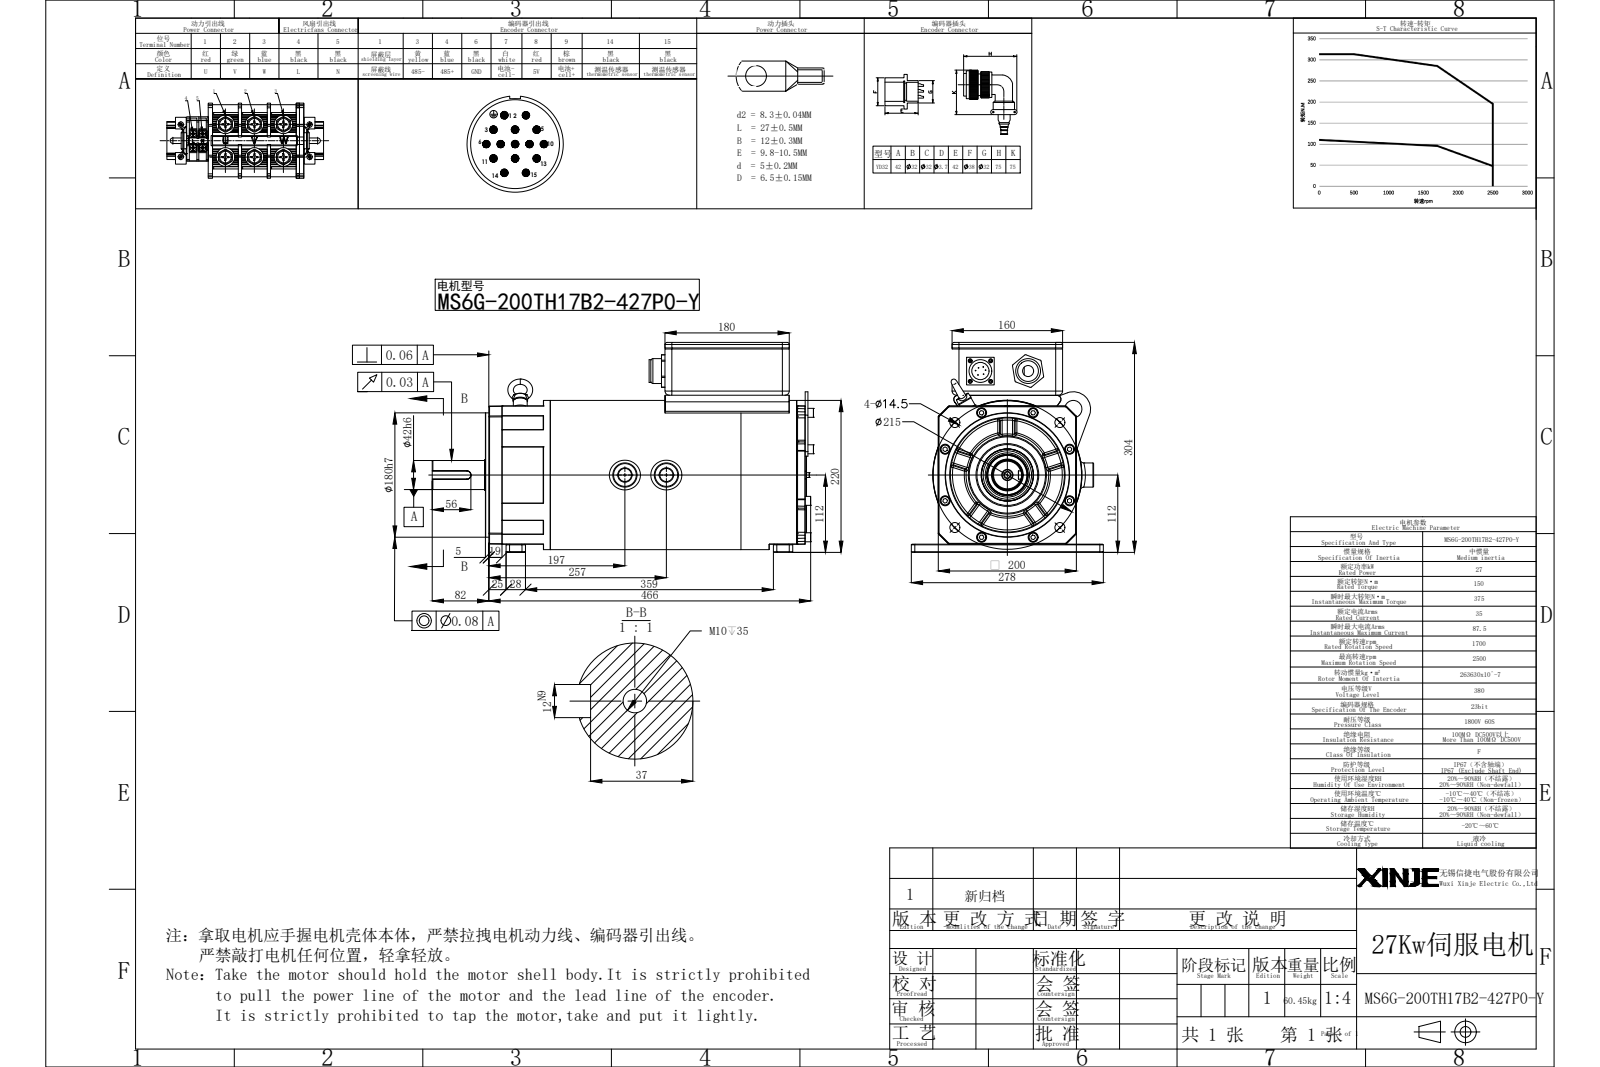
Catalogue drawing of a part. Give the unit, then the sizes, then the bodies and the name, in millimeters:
Units: millimetres
Overall size (bounding box): 552 × 304 × 278
Round holes (diameter × count): ⌀14.5 ×12, ⌀6.8 ×10, ⌀10 ×8, ⌀13 ×8, ⌀4 ×4, ⌀4.5 ×4, ⌀5 ×4, ⌀6.6 ×4, ⌀7 ×4, ⌀11.5 ×4, ⌀8.6 ×2, ⌀19 ×2
Round bosses / shafts (diameter × count): ⌀8 ×9, ⌀13 ×8, ⌀7 ×8, ⌀6 ×8, ⌀1 ×6, ⌀13.44 ×4, ⌀10 ×4, ⌀4 ×4
Partial cylindrical surfaces — rounded edges, fillets, slot ends (radius × count): R3 ×24, R2 ×14, R10 ×10, R6 ×9, R1 ×8, R5.76 ×8, R5 ×6, R5.3 ×6
Main face-to-face distances: 276, 12, 2, 11, 1, 428, 440, 369, 93, 358
Hole centre spacings: 37.31, 41.18, 77.29, 97.5, 104.36, 114.19, 137.89, 155.96
Volume: 20 170 000 mm³ · Surface area: 1 155 000 mm²
Bodies: 51 solids, 1868 faces (610 planar, 481 cylindrical, 777 other)
Part name (STEP PRODUCT): MS6G-200TH17B2-427P0-Y
STEP written by: SolidWorks 2022 (CONFIG_CONTROL_DESIGN)
